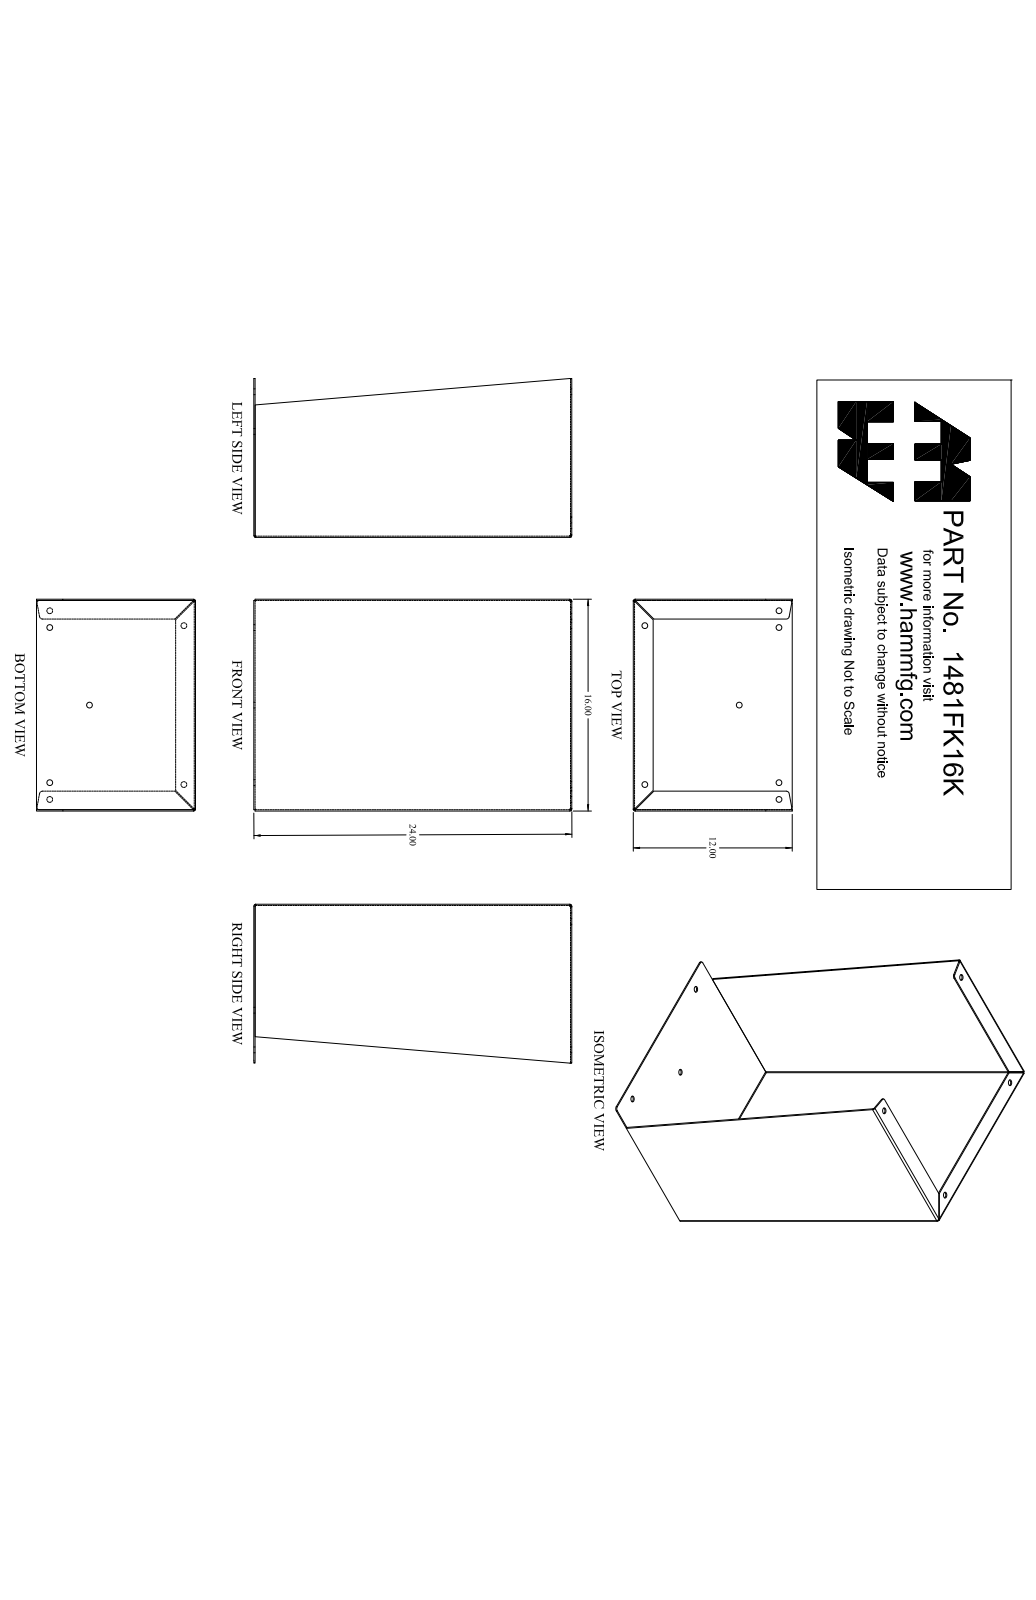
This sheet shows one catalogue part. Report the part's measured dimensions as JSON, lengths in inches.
{"part_name": "1481FK16K_Default", "step_written_by": "SolidWorks 2019 (CONFIG_CONTROL_DESIGN)", "units": "inches", "bodies": {"solids": 1, "faces": 78, "planar": 42, "cylindrical": 30, "other": 6}, "overall_size": [24, 16, 12], "volume_in3": 108.3, "surface_area_in2": 2295, "round_holes": [[0.437, 7]], "partial_cylinders_radius": [[0.048, 6], [0.143, 6], [0.22, 4]], "face_to_face_distances": [0.095, 15.905, 15.81, 16, 0.095, 23.81, 23.905, 23.905, 24, 1.405], "hole_center_spacings": [1.266, 6.582, 7.731, 9.315, 10.126, 10.187, 12.984, 15.593]}
